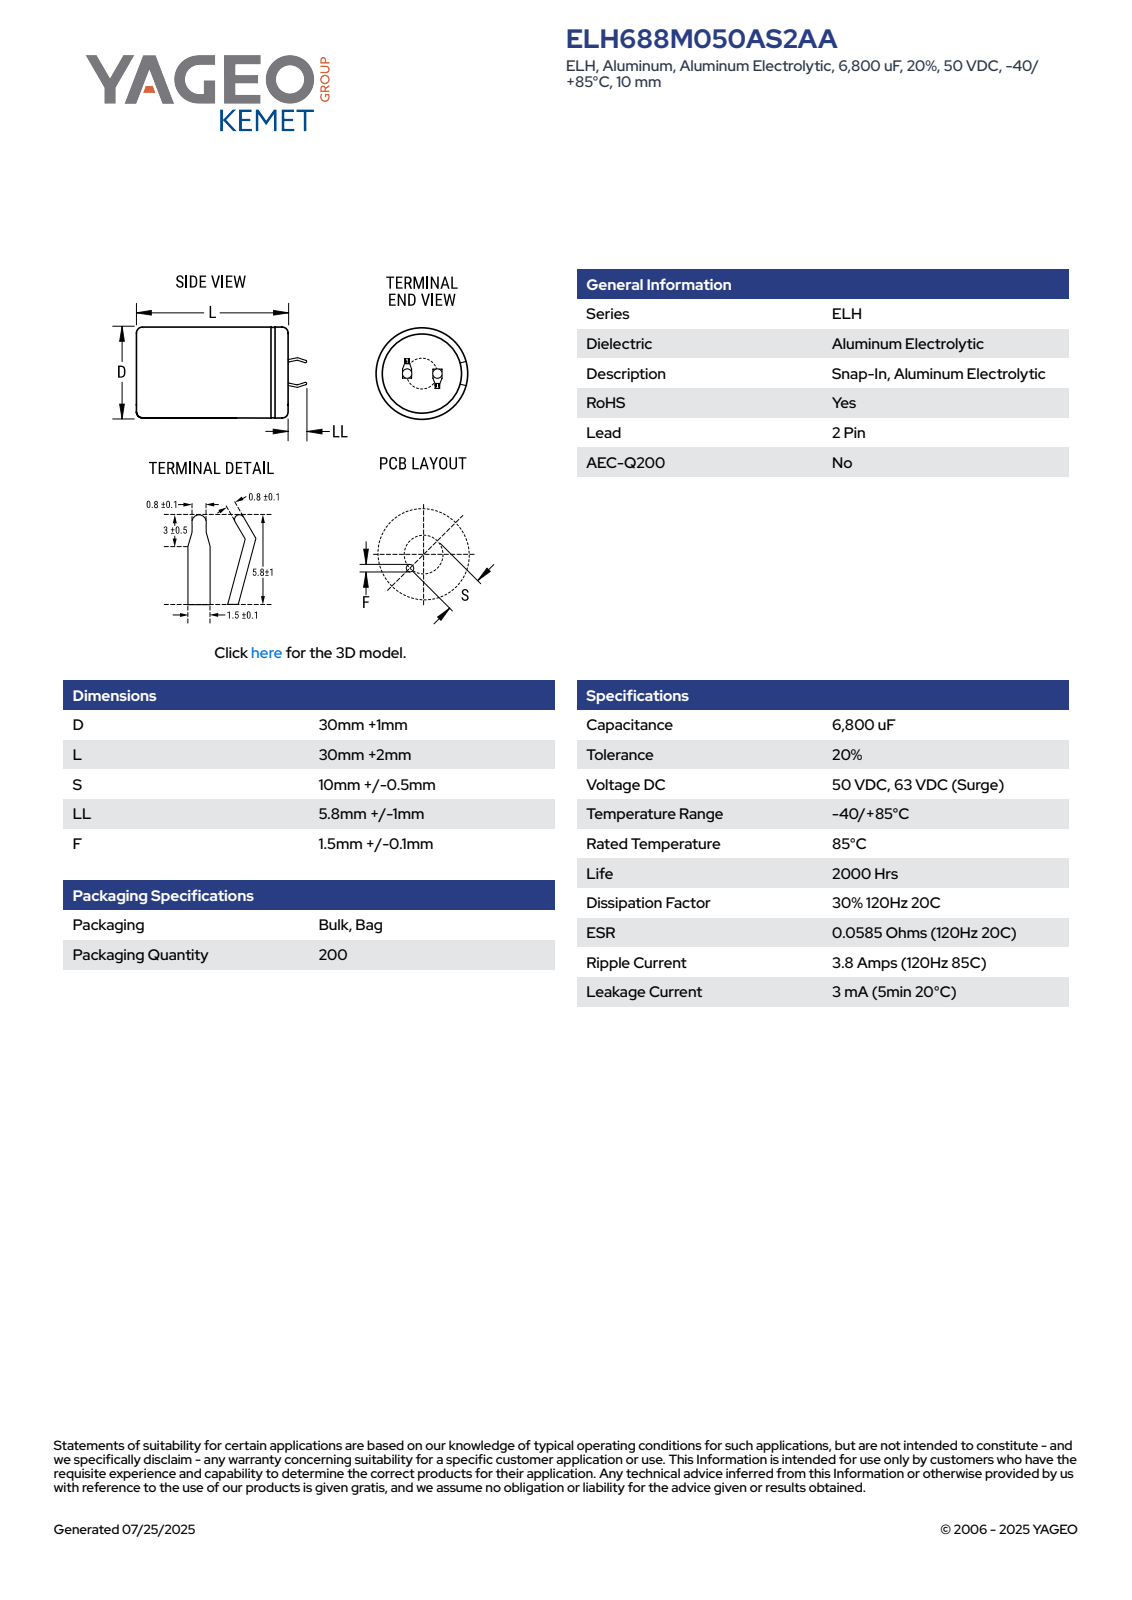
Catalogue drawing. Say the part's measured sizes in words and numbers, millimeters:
The part is named "CARS_K2P_30X30_D31L32S10LL6.8F1.6". Its 3-D file was written by "SolidWorks 2014 (AUTOMOTIVE_DESIGN)". It is 1 solid with 100 faces: 52 planar, 9 cylindrical and 39 other. Overall it measures 38.79 by 31 by 31 millimeters. Its volume is 23 819 cubic millimeters and its surface area 4 634 square millimeters. Round holes: 1 of diameter 27.43. Round bosses or shafts: 1 of diameter 31. Partial cylindrical surfaces (rounded edges, fillets, slot ends): 1 of radius 15.49. The main face-to-face distances are 31.99, 0.6, 32.49, 0.5, 7.08, 7.63, 0.75, 1.35, 7.68, 6.48.
